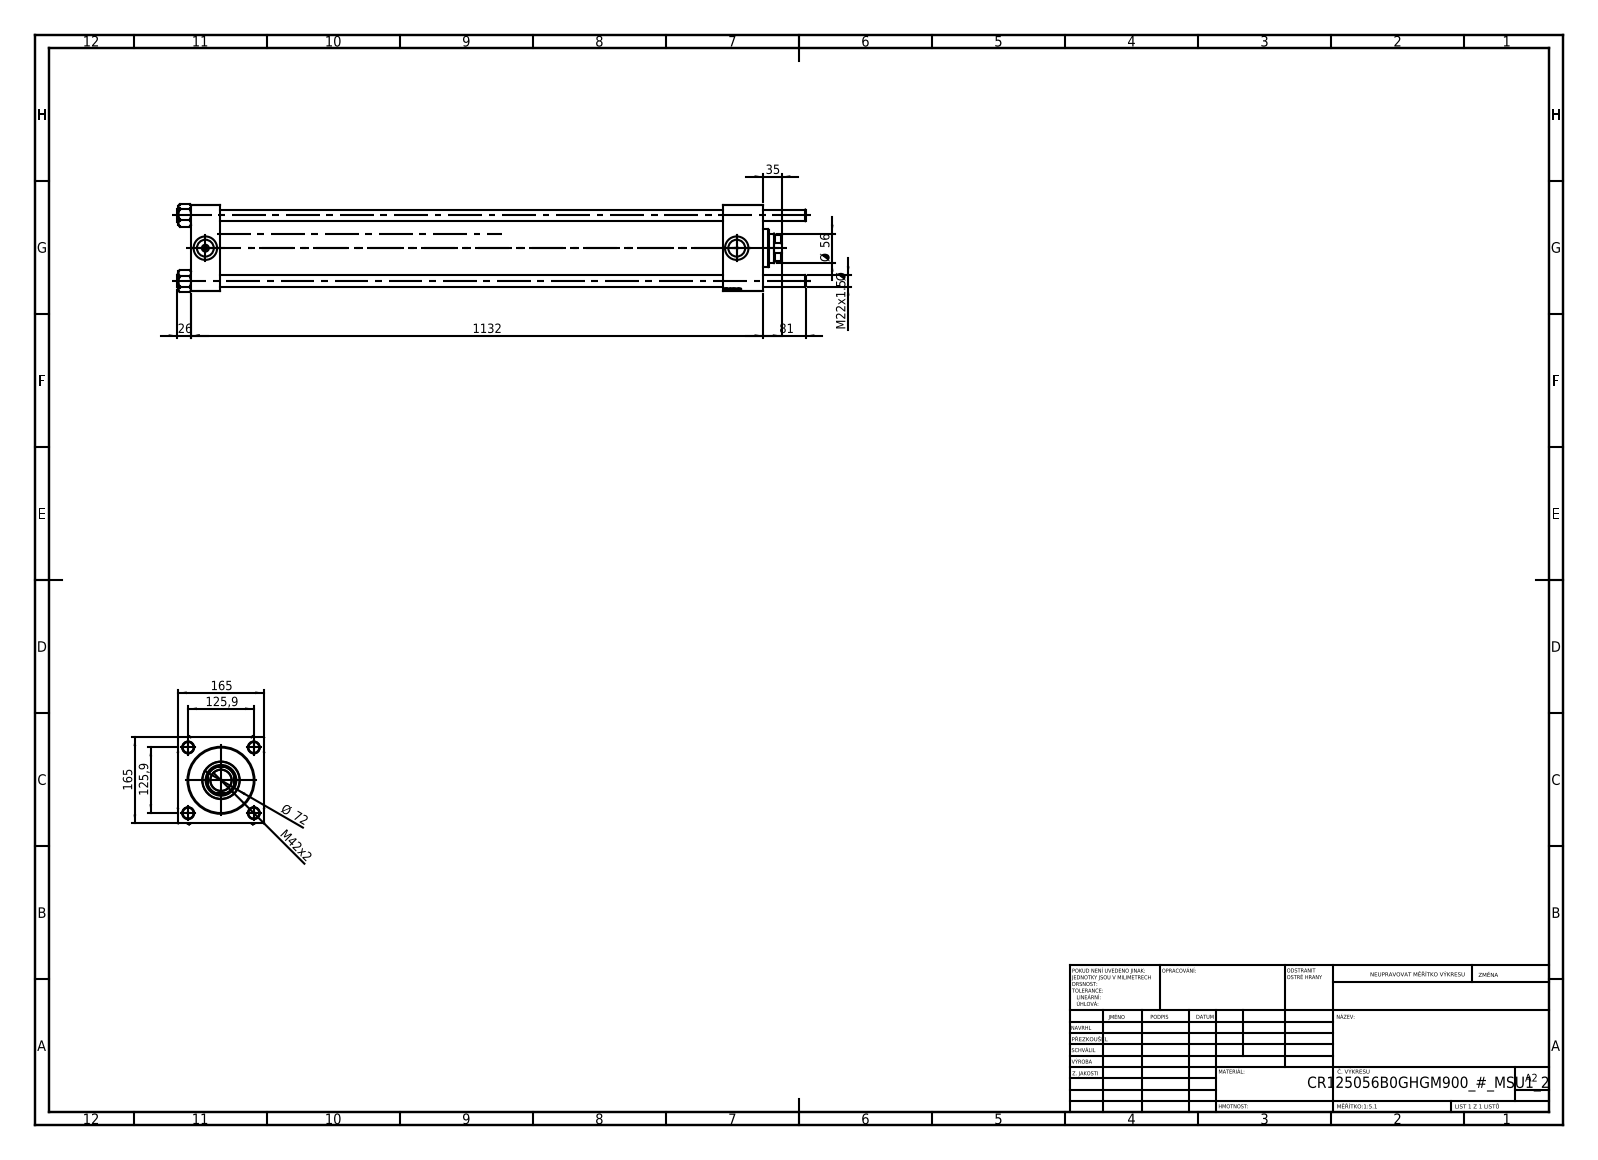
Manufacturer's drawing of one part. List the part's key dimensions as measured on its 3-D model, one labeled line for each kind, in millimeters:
Part name (STEP PRODUCT): V215CR_VCP_B; NUT_M5_B; V215_VC_A; V215CR_B_TYCINKA (+1 more)
STEP written by: SolidWorks 2019 (CONFIG_CONTROL_DESIGN)
Units: millimetres
Bodies: 11 solids, 1206 faces (480 planar, 78 cylindrical, 648 other)
Overall size (bounding box): 1204 × 168.98 × 165.07
Volume: 9 248 000 mm³ · Surface area: 1 654 000 mm²
Round holes (diameter × count): ⌀22 ×4, ⌀7 ×2, ⌀32.24 ×2, ⌀45 ×2, ⌀40.5 ×1, ⌀56 ×1, ⌀59 ×1, ⌀96 ×1, ⌀125 ×1, ⌀125.5 ×1
Round bosses / shafts (diameter × count): ⌀25 ×4, ⌀131 ×1, ⌀72 ×1
Partial cylindrical surfaces — rounded edges, fillets, slot ends (radius × count): R27 ×1
Main face-to-face distances: 165, 55, 1097, 1042, 1019, 964, 78, 1068.3, 1013.3, 49.3
Hole centre spacings: 89.02, 125.9, 178.05, 1018.5
